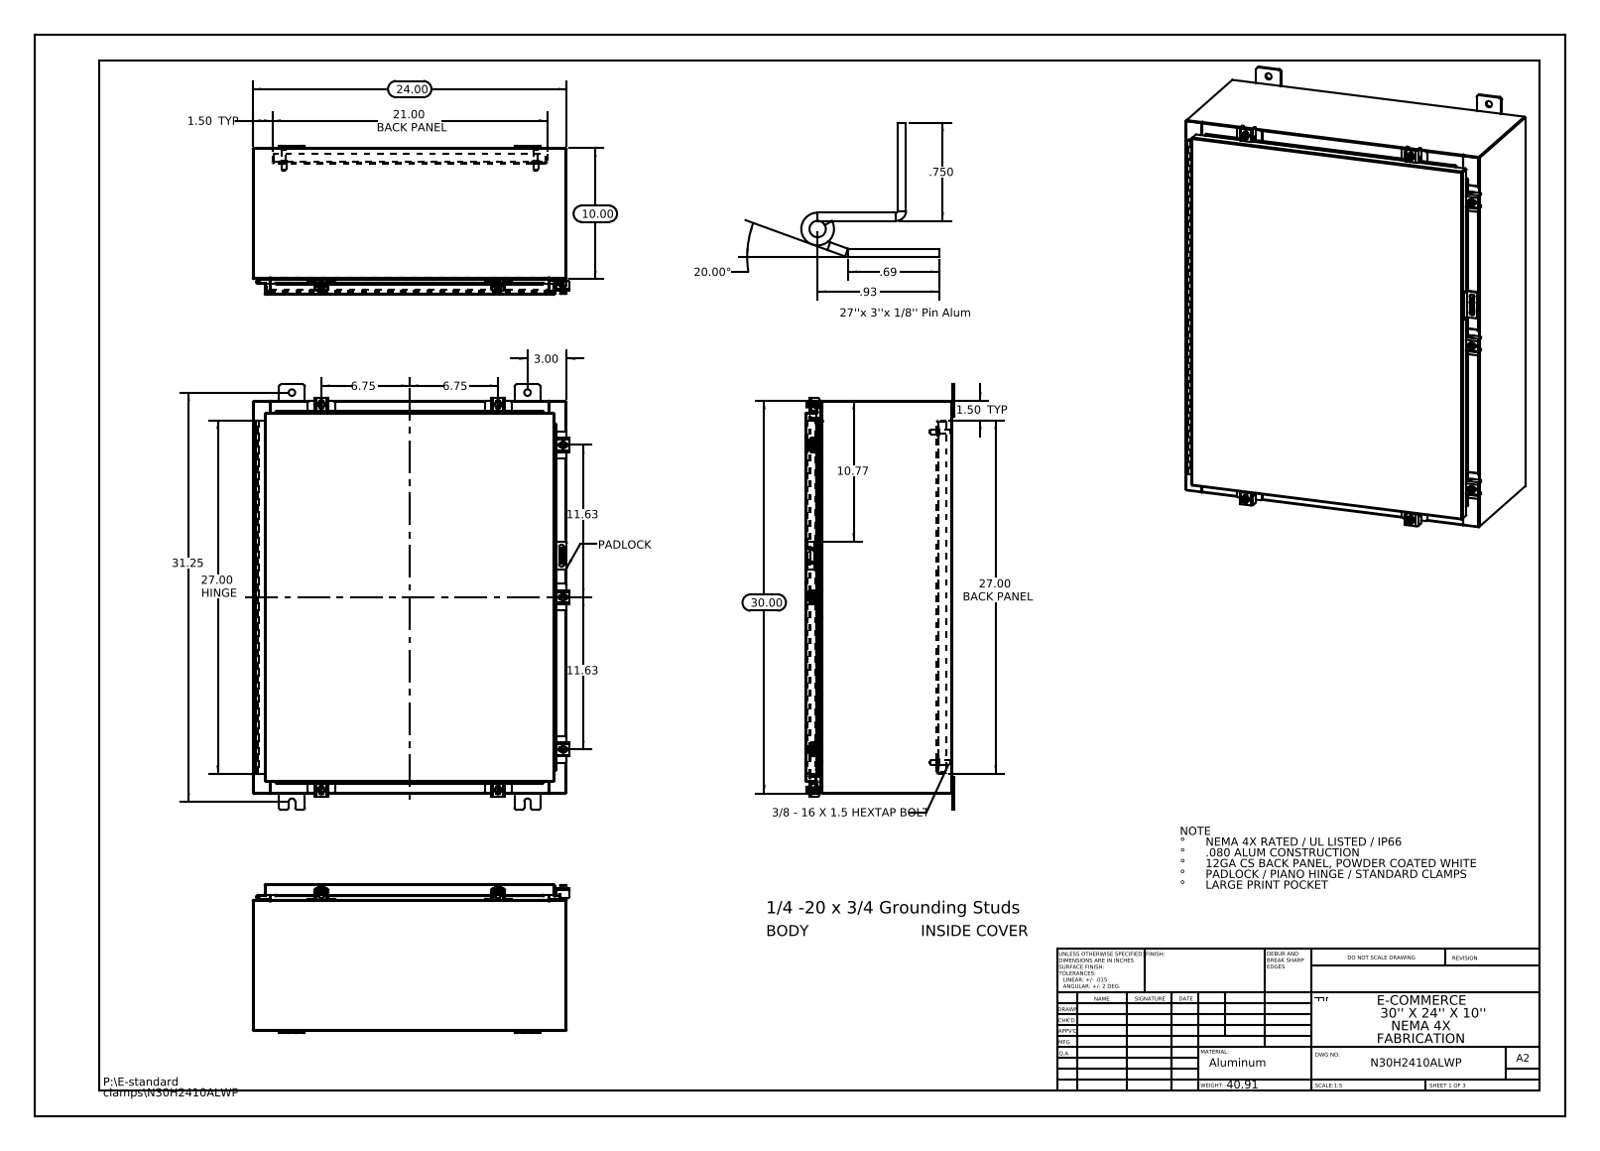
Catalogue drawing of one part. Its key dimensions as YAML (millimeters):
part_name: "N30H2410ALWP Clamp Top; N30H2410ALWP Body; N30H2410ALWP Backpanel; N30H2410ALWP Top (+8 more)"
step_written_by: "SolidWorks 2013 (CONFIG_CONTROL_DESIGN)"
units: millimeters
bodies: {solids: 52, faces: 1990, planar: 1056, cylindrical: 830, other: 104}
overall_size: [825.5, 615, 289.3]
volume: 4603000
surface_area: 4548000
round_holes:
  - {diameter: 12.7, count: 8}
  - {diameter: 5.4, count: 7}
  - {diameter: 6.6, count: 7}
  - {diameter: 3.2, count: 2}
  - {diameter: 3.2, count: 1}
round_bosses_or_shafts:
  - {diameter: 6.4, count: 8}
  - {diameter: 12.7, count: 7}
  - {diameter: 10.1, count: 7}
  - {diameter: 15.9, count: 4}
  - {diameter: 9.5, count: 4}
  - {diameter: 8.4, count: 4}
partial_cylinders:
  - {radius: 1.5, count: 34}
  - {radius: 0.3, count: 27}
  - {radius: 4.8, count: 24}
  - {radius: 2.2, count: 21}
  - {radius: 3, count: 14}
  - {radius: 3.6, count: 14}
  - {radius: 1.3, count: 11}
  - {radius: 2, count: 10}
face_to_face_distances: [1.9, 282.6, 284.5, 280.7, 2.6, 607.7, 25.4, 27.3, 255.3, 257.2]
hole_center_spacings: [698.5, 809.7, 47.2, 57.8, 59.1, 61.5, 90.4, 90.4]
